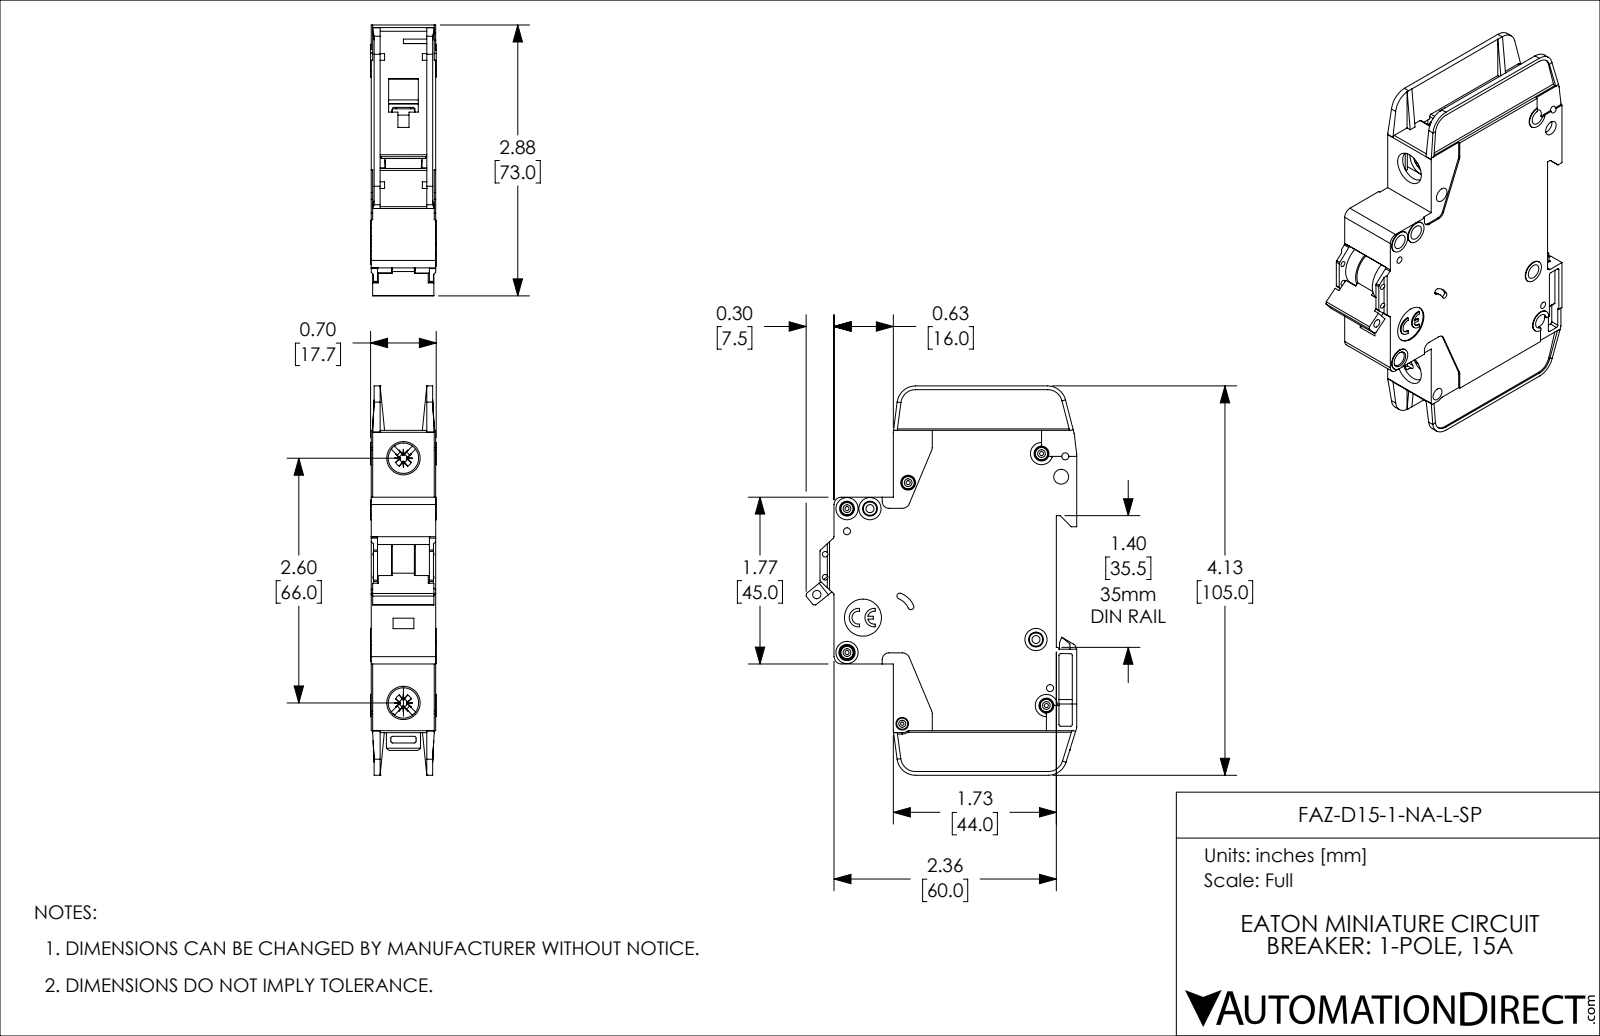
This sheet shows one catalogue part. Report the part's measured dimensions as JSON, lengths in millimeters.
{"part_name": "FAZ-D15-1-NA-L-SP", "step_written_by": "SolidWorks 2019 (AUTOMOTIVE_DESIGN)", "units": "millimeters", "bodies": {"solids": 1, "faces": 1127, "planar": 671, "cylindrical": 357, "other": 99}, "overall_size": [105, 73.1, 17.7], "volume_mm3": 76720, "surface_area_mm2": 26460, "round_holes": [[4, 8], [1.1, 5], [1.9, 4], [1.5, 2], [2.2, 2], [8.2, 2], [0.9, 1], [2.3, 1], [2.5, 1], [3.4, 1], [10, 1]], "round_bosses_or_shafts": [[3.3, 5], [6, 4], [3, 2], [2.5, 1]], "partial_cylinders_radius": [[0.5, 42], [0.4, 10], [1, 10], [2, 8], [5, 5], [0.2, 4], [0.7, 4], [1.1, 4]], "face_to_face_distances": [1.2, 17.4, 15, 16.2, 2.4, 13.8, 0.4, 0.8, 12.6, 14.6], "hole_center_spacings": [6.2, 13.6, 22.1, 4.8, 5.1, 5.2, 5.6, 6.1]}
